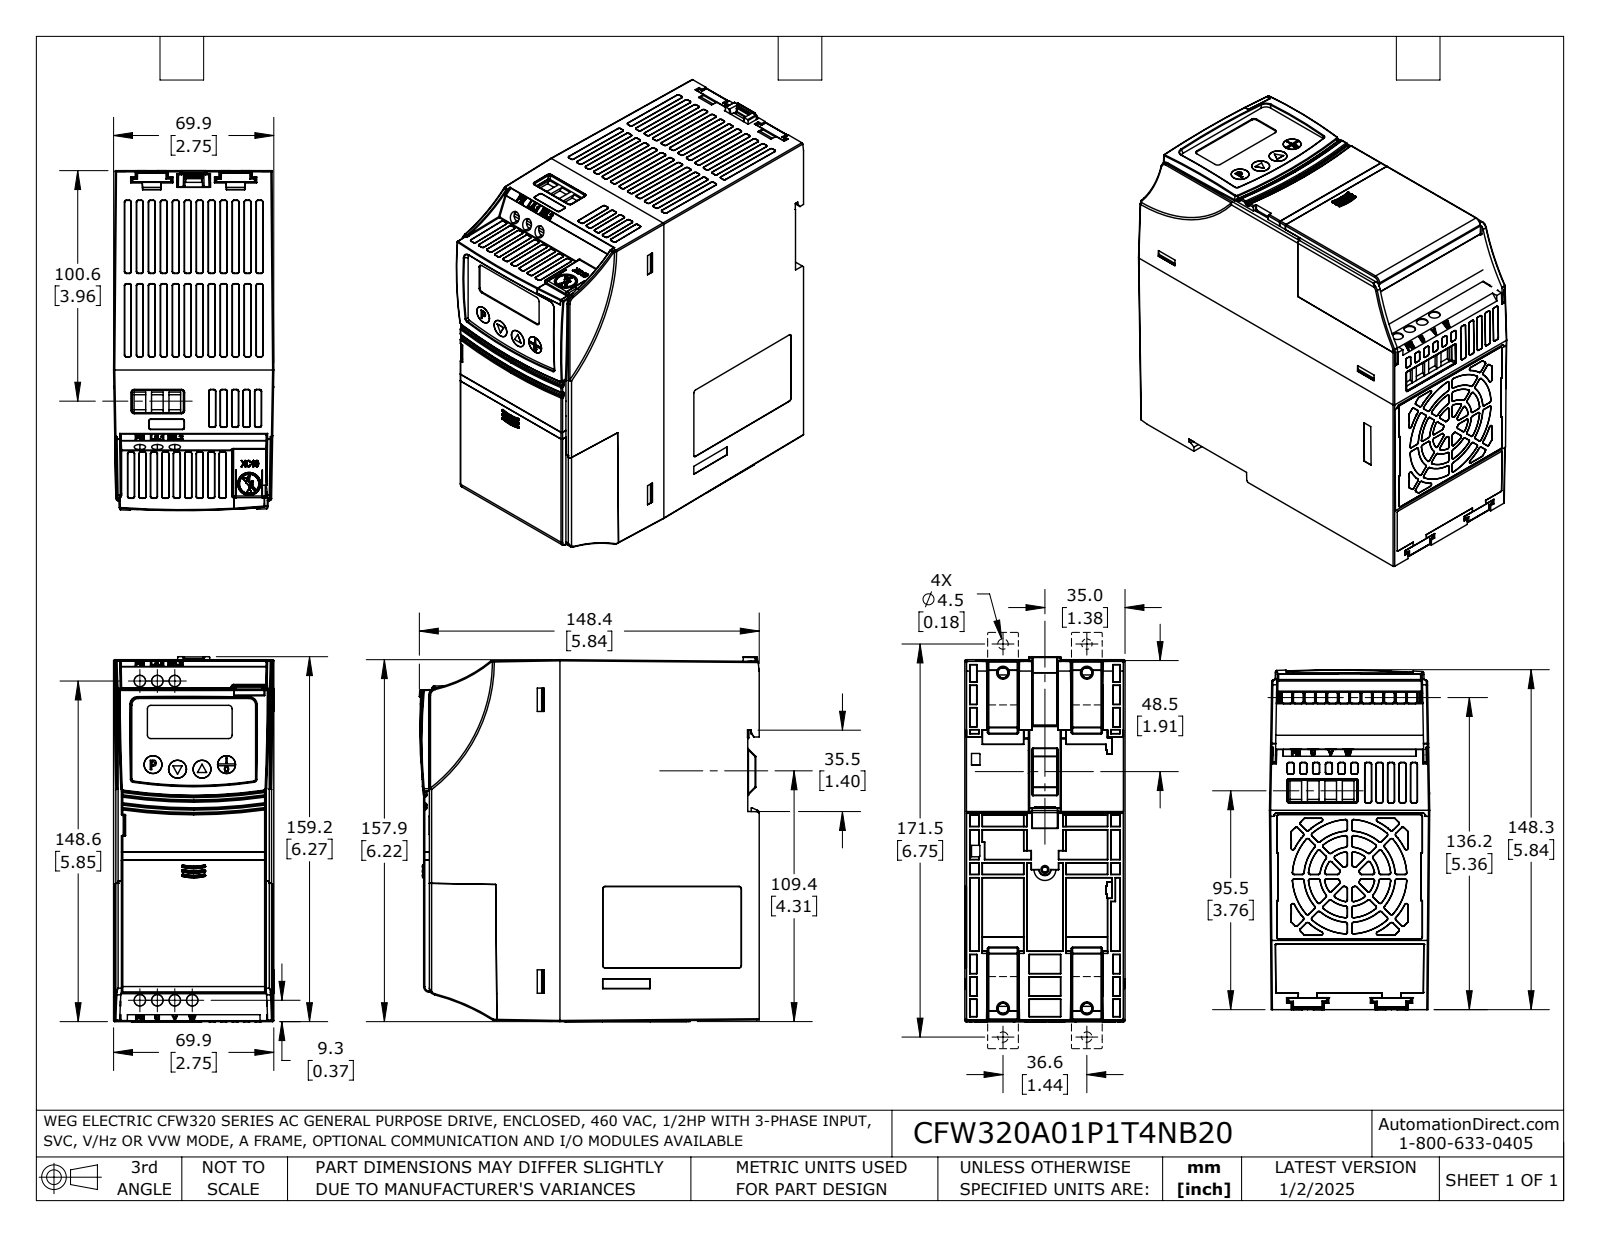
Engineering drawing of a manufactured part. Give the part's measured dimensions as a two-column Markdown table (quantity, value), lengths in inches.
| quantity | value |
| --- | --- |
| part name | CFW320A01P1T4NB20 |
| STEP written by | SolidWorks 2021 (AUTOMOTIVE_DESIGN) |
| units | inches |
| bodies | 6 solids, 3715 faces (1587 planar, 853 cylindrical, 1275 other) |
| overall size | 6.269 × 5.841 × 2.754 |
| volume | 15.24 in³ |
| surface area | 309 in² |
| round holes (diameter × count) | 0.197 × 3 |
| partial cylindrical surfaces (radius × count) | 0.012 × 327, 0.02 × 150, 0.039 × 13, 0.03 × 5, 0.118 × 3, 0.01 × 2, 0.098 × 1, 0.126 × 1 |
| main face-to-face distances | 0.07, 0.055, 0.019, 0.05, 6, 5.33, 5.275, 5.571, 5.516, 0.241 |
| hole center spacings | 0.3, 0.6 |
